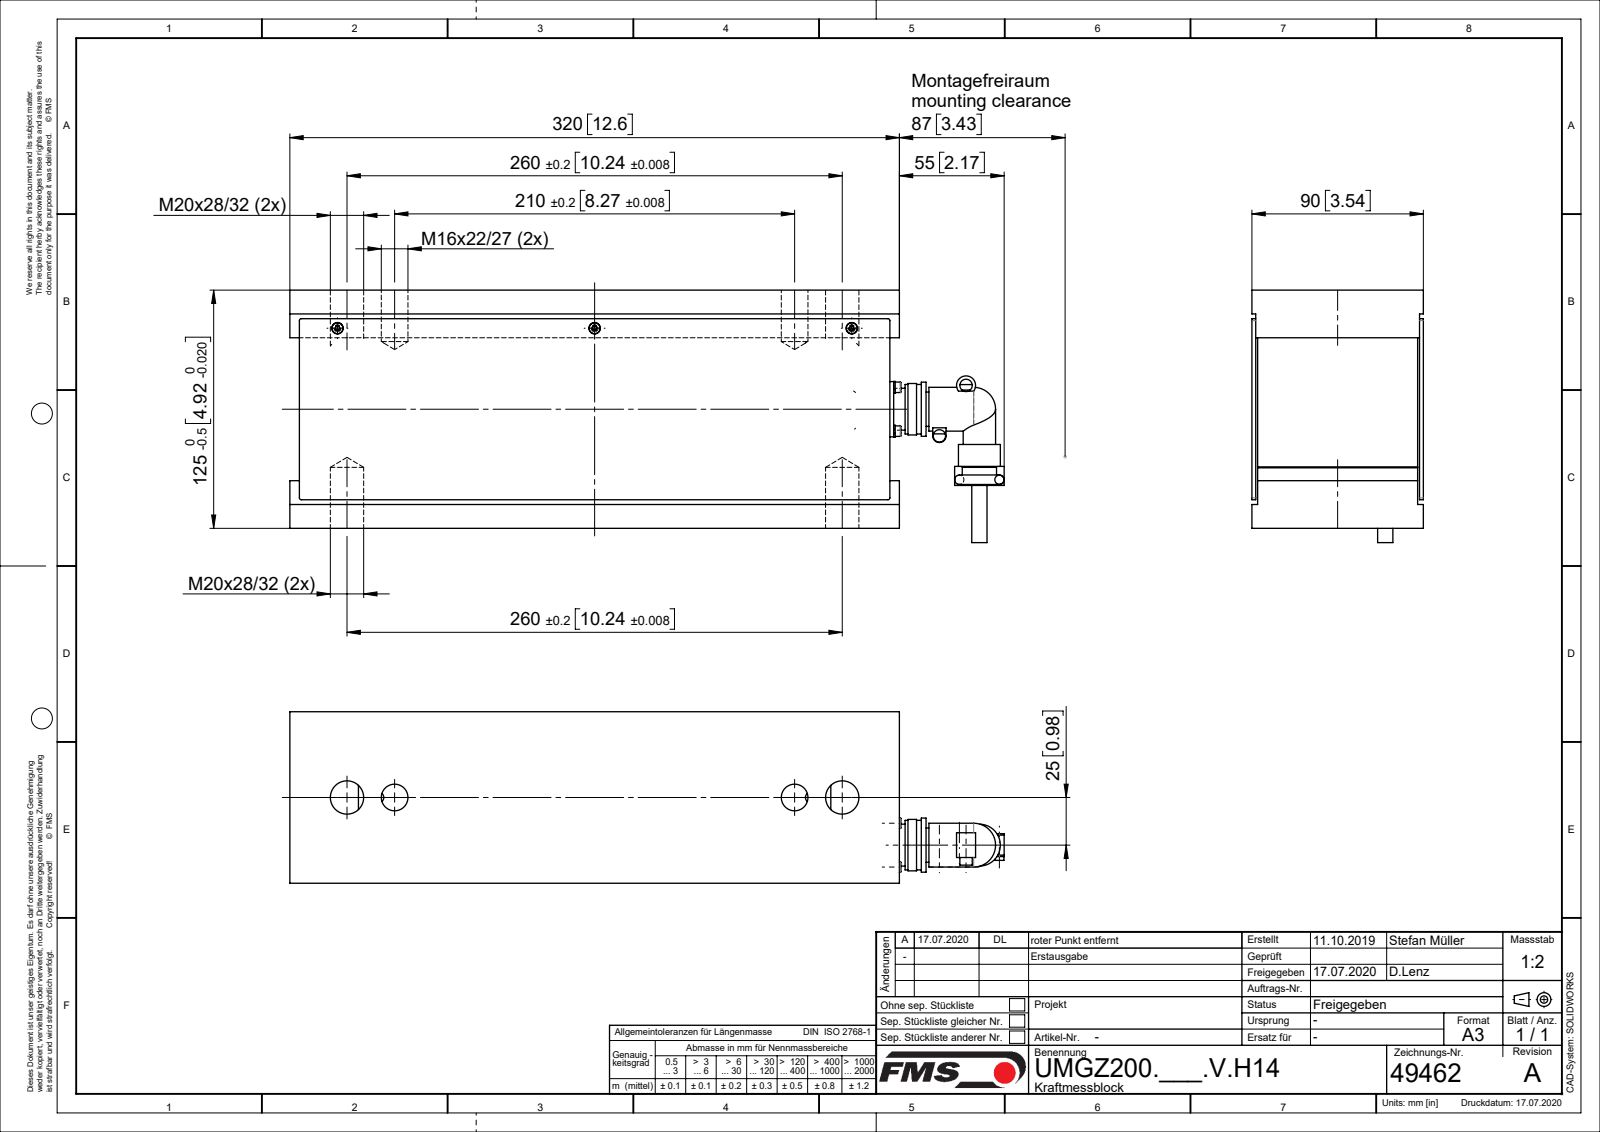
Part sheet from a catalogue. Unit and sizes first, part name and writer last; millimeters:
Units: millimetres
Overall size (bounding box): 375 × 132.5 × 90
Round holes (diameter × count): ⌀2.6 ×7, ⌀3.5 ×4, ⌀3.6 ×3, ⌀6 ×3, ⌀14.21 ×2, ⌀17.74 ×2, ⌀23 ×1
Round bosses / shafts (diameter × count): ⌀22 ×2, ⌀6.5 ×2, ⌀4.8 ×2, ⌀28.4 ×1, ⌀27 ×1, ⌀26 ×1, ⌀18 ×1, ⌀17 ×1
Partial cylindrical surfaces — rounded edges, fillets, slot ends (radius × count): R2.5 ×2, R3.5 ×1, R5 ×1
Main face-to-face distances: 2, 88, 85, 3, 87, 1, 90, 86, 125, 84
Hole centre spacings: 16.26, 23, 25, 32.53, 135, 235, 210, 260
Volume: 3 454 000 mm³ · Surface area: 306 772 mm²
Bodies: 4 solids, 230 faces (81 planar, 102 cylindrical, 47 other)
Part name (STEP PRODUCT): U49462; U4945804; TEIL1; FLANSCHDOSE_WINKEL_AMPH_4-POLIG (+2 more)
STEP written by: Mechanical Desktop 2007 (CONFIG_CONTROL_DESIGN)
